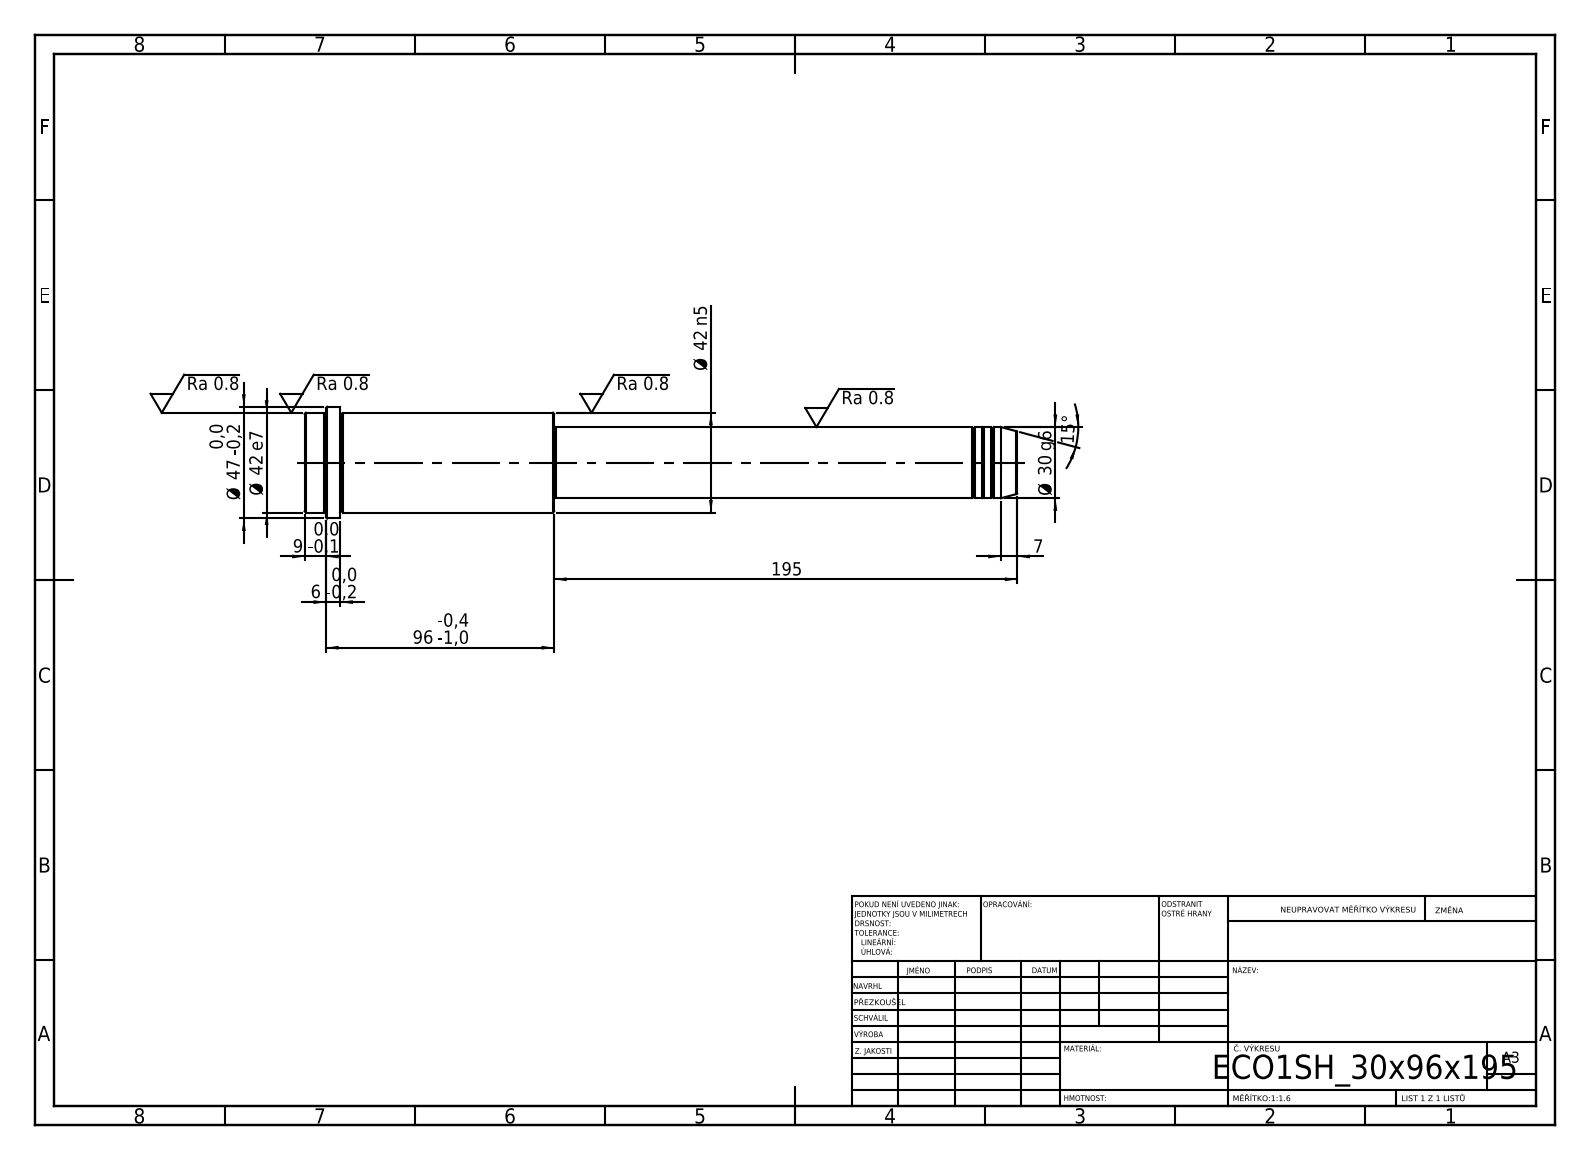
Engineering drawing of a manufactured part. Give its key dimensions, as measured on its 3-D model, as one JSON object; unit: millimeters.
{"step_written_by": "SolidWorks 2019 (CONFIG_CONTROL_DESIGN)", "units": "millimeters", "bodies": {"solids": 1, "faces": 52, "planar": 6, "cylindrical": 16, "other": 30}, "overall_size": [300, 47, 47], "volume_mm3": 284501, "surface_area_mm2": 35867, "round_bosses_or_shafts": [[47, 1], [42, 1], [30, 1], [29, 1]], "face_to_face_distances": [105, 195, 300, 285, 90, 15, 291, 96, 6, 9]}
